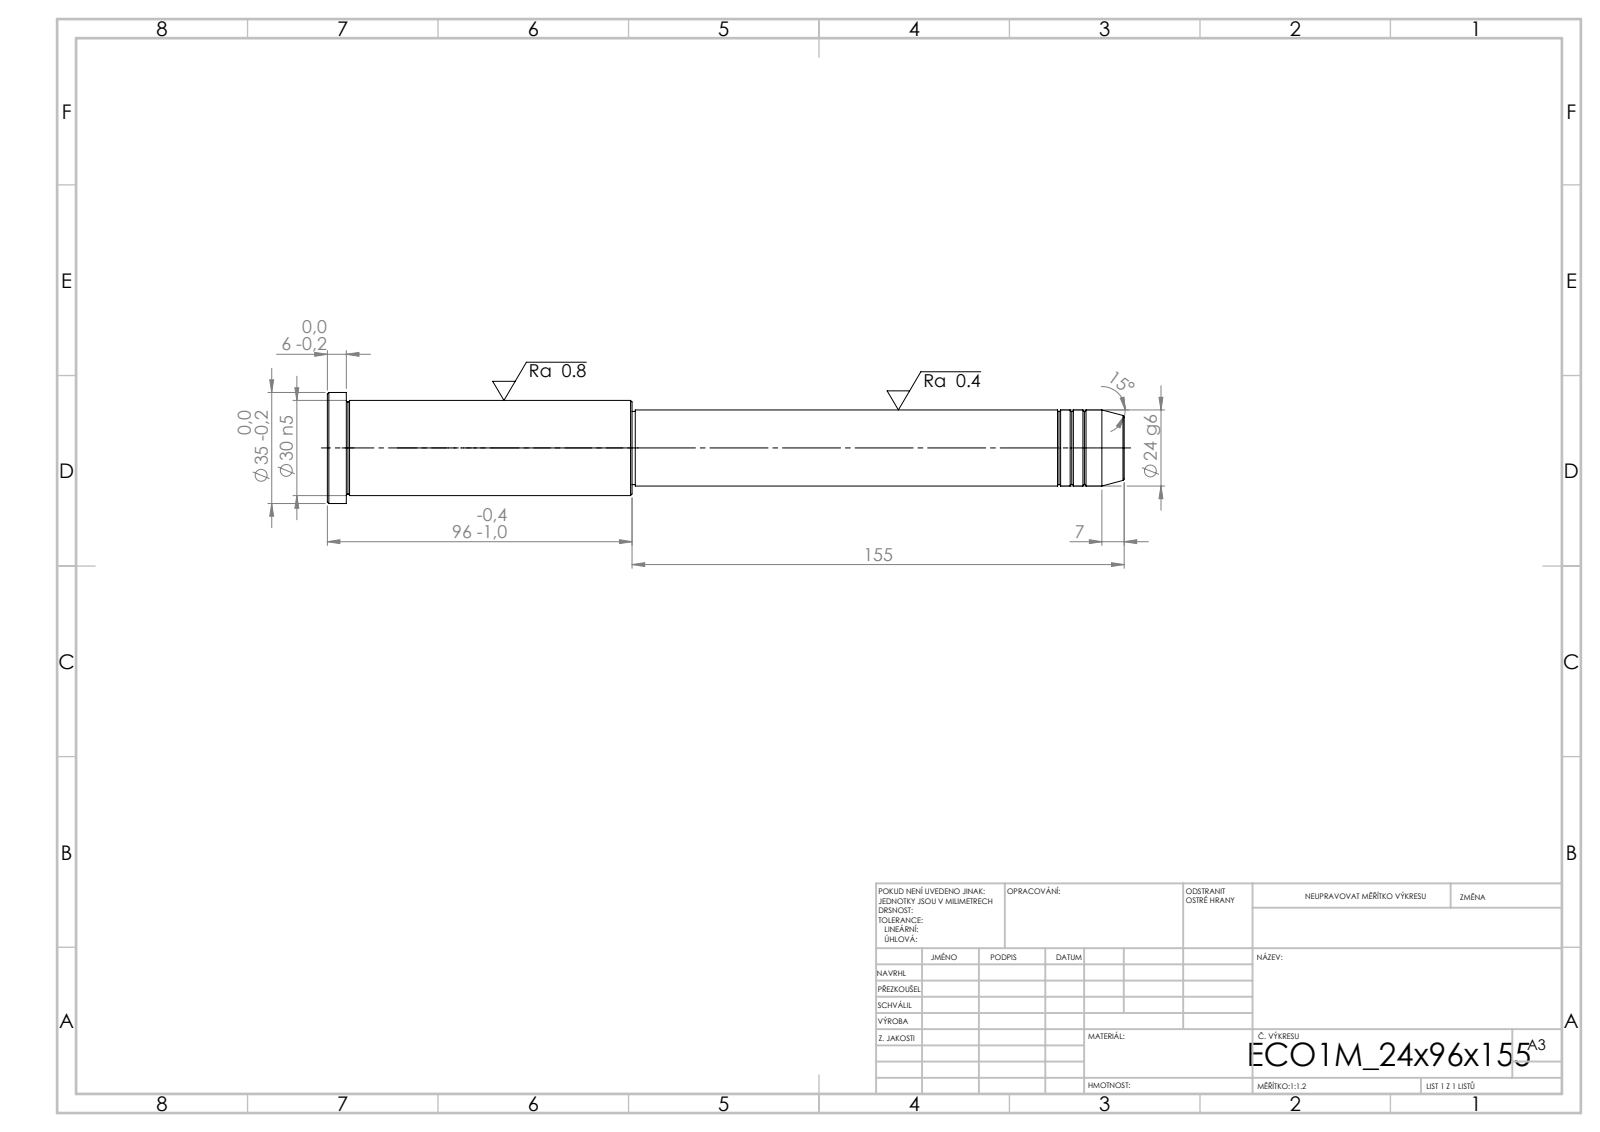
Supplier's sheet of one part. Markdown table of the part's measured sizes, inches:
| quantity | value |
| --- | --- |
| STEP written by | SolidWorks 2019 (CONFIG_CONTROL_DESIGN) |
| units | inches |
| bodies | 1 solid, 43 faces (5 planar, 14 cylindrical, 24 other) |
| overall size | 9.882 × 1.378 × 1.378 |
| volume | 8.473 in³ |
| surface area | 35.3 in² |
| round bosses / shafts (diameter × count) | 1.378 × 1, 1.181 × 1, 0.945 × 1, 0.906 × 1 |
| main face-to-face distances | 9.882, 9.646, 0.236, 6.102, 3.543, 3.78, 6.063, 0.039, 3.583, 3.819 |
